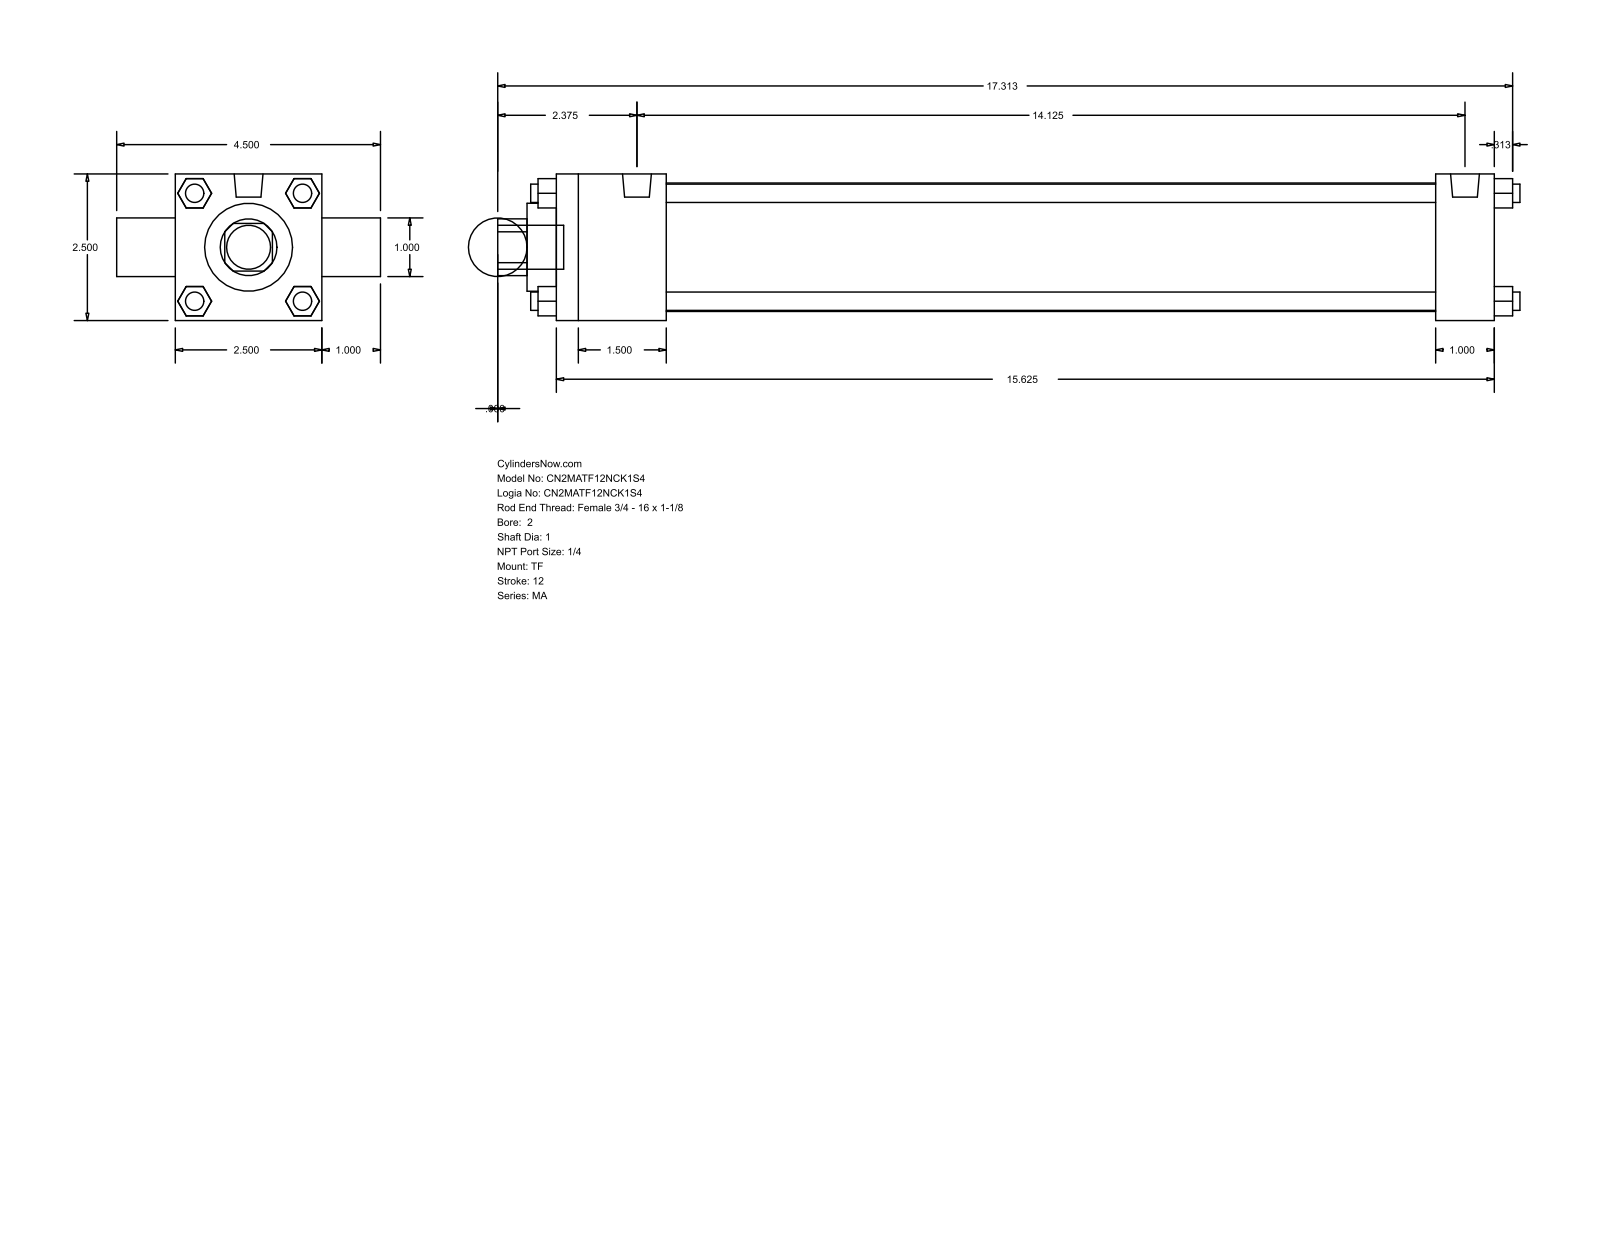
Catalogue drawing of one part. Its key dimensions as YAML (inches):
part_name: "MA_TF__0200_1"
step_written_by: "GSSL Pune (CONFIG_CONTROL_DESIGN)"
units: inches
bodies: {solids: 0, faces: 120, planar: 92, cylindrical: 28, other: 0}
overall_size: [17.437, 4.5, 2.5]
round_holes:
  - {diameter: 1, count: 2}
  - {diameter: 1.5, count: 1}
  - {diameter: 2.19, count: 1}
round_bosses_or_shafts:
  - {diameter: 0.313, count: 7}
  - {diameter: 0.492, count: 2}
  - {diameter: 0.75, count: 1}
partial_cylinders:
  - {radius: 0.484, count: 1}
face_to_face_distances: [2.5, 1, 16, 0.5, 1.875, 15, 13.125, 14.125, 3.5, 0.92]
